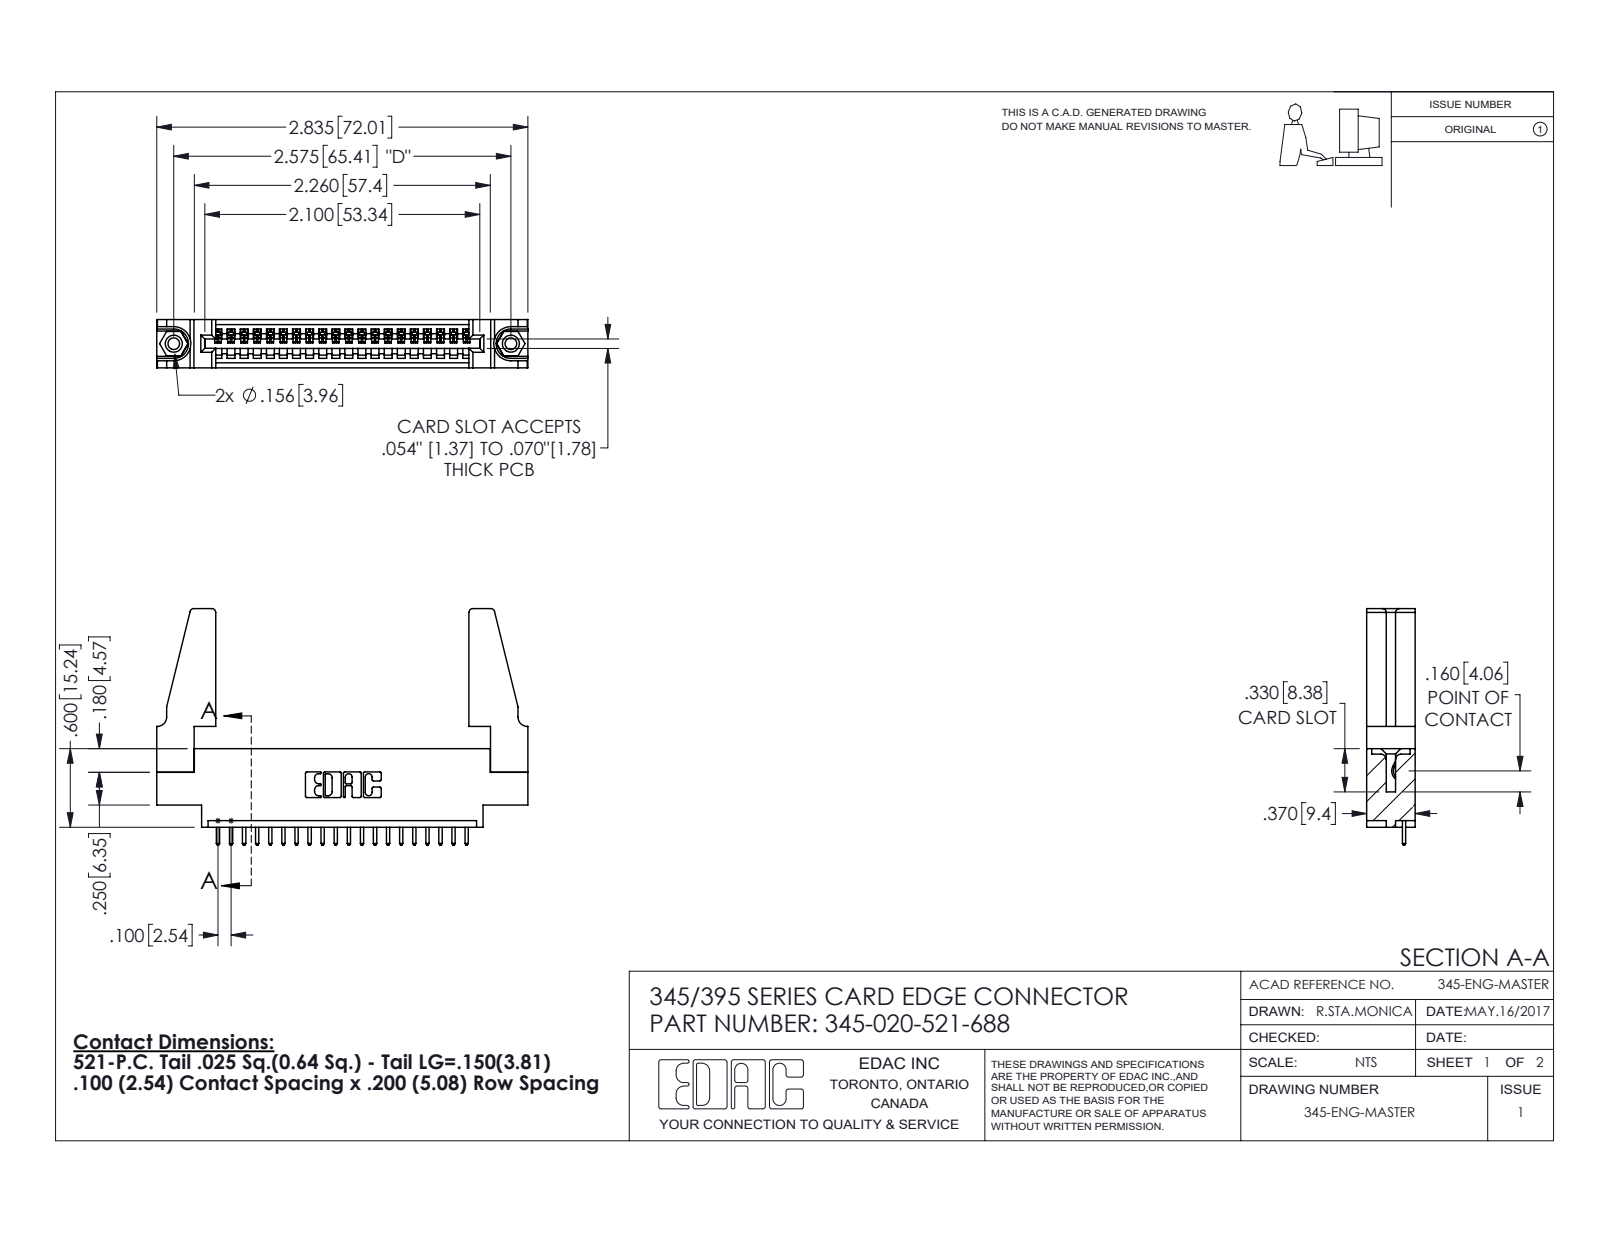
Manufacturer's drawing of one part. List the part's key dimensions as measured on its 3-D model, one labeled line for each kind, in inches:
Part name (STEP PRODUCT): 345-220-078_345-220-088; 345-020-521-688; 345 Part_0.170 Offset - 0.156 Dia-TH; 345-292-001_345-293-121 (+1 more)
STEP written by: SolidWorks 2016 (CONFIG_CONTROL_DESIGN)
Units: inches
Bodies: 25 solids, 1414 faces (956 planar, 442 cylindrical, 16 other)
Overall size (bounding box): 2.836 × 1.807 × 0.37
Volume: 0.595 in³ · Surface area: 17.61 in²
Round holes (diameter × count): ⌀0.089 ×2, ⌀0.125 ×2, ⌀0.156 ×2, ⌀0.064 ×1
Round bosses / shafts (diameter × count): ⌀0.155 ×2
Partial cylindrical surfaces — rounded edges, fillets, slot ends (radius × count): R0.006 ×40, R0.01 ×40, R0.01 ×22, R0.03 ×8, R0.007 ×6, R0.031 ×6, R0.026 ×3, R0.031 ×2
Main face-to-face distances: 0.37, 0.072, 0.298, 0.2, 0.098, 0.272, 0.025, 0.225, 0.175, 0.15
Hole centre spacings: 0.27, 2.341, 2.575
